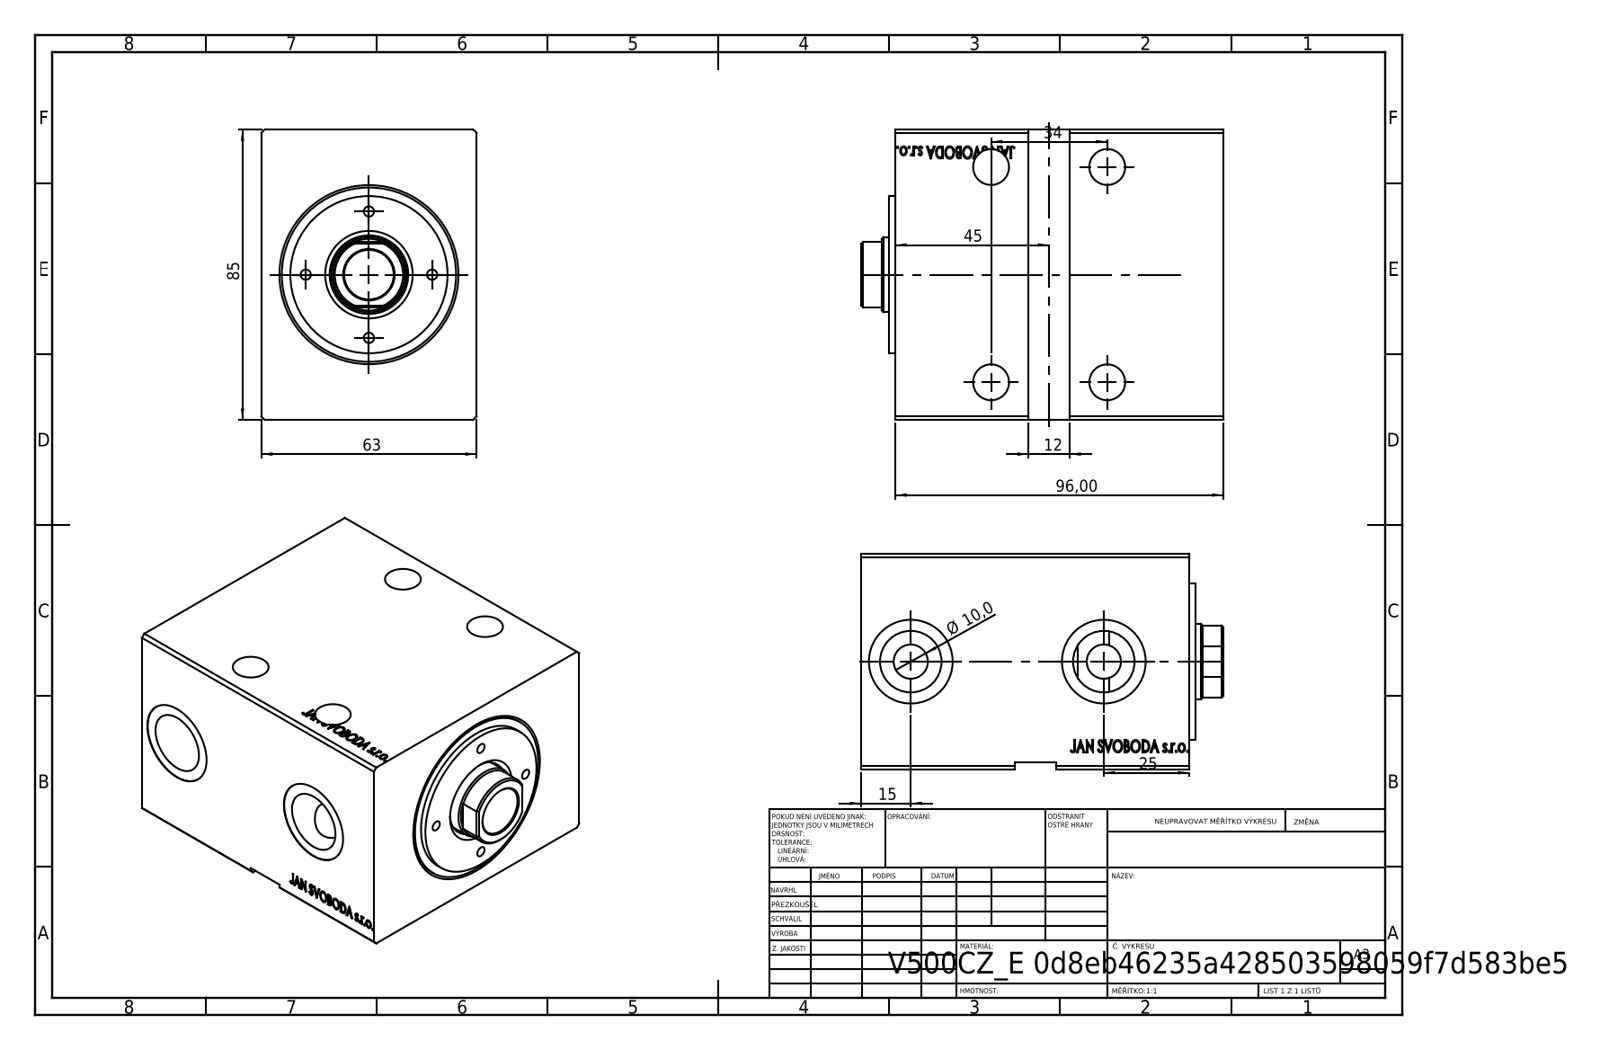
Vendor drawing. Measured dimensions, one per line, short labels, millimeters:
written by: SolidWorks 2019 (CONFIG_CONTROL_DESIGN)
unit: mm
bodies: 1 solid, 774 faces (381 planar, 27 cylindrical, 366 other)
size: 96 × 85 × 63
volume: 325 107 mm³; area: 60 669 mm²
holes: 4× ⌀10.5, 2× ⌀10, 2× ⌀18, 2× ⌀24.5, 1× ⌀36, 1× ⌀40, 1× ⌀51
face distances: 63, 85, 96, 81.3, 14.7, 2, 61, 95.8, 14.5, 25
hole spacings: 34, 63, 71.59, 56.5
